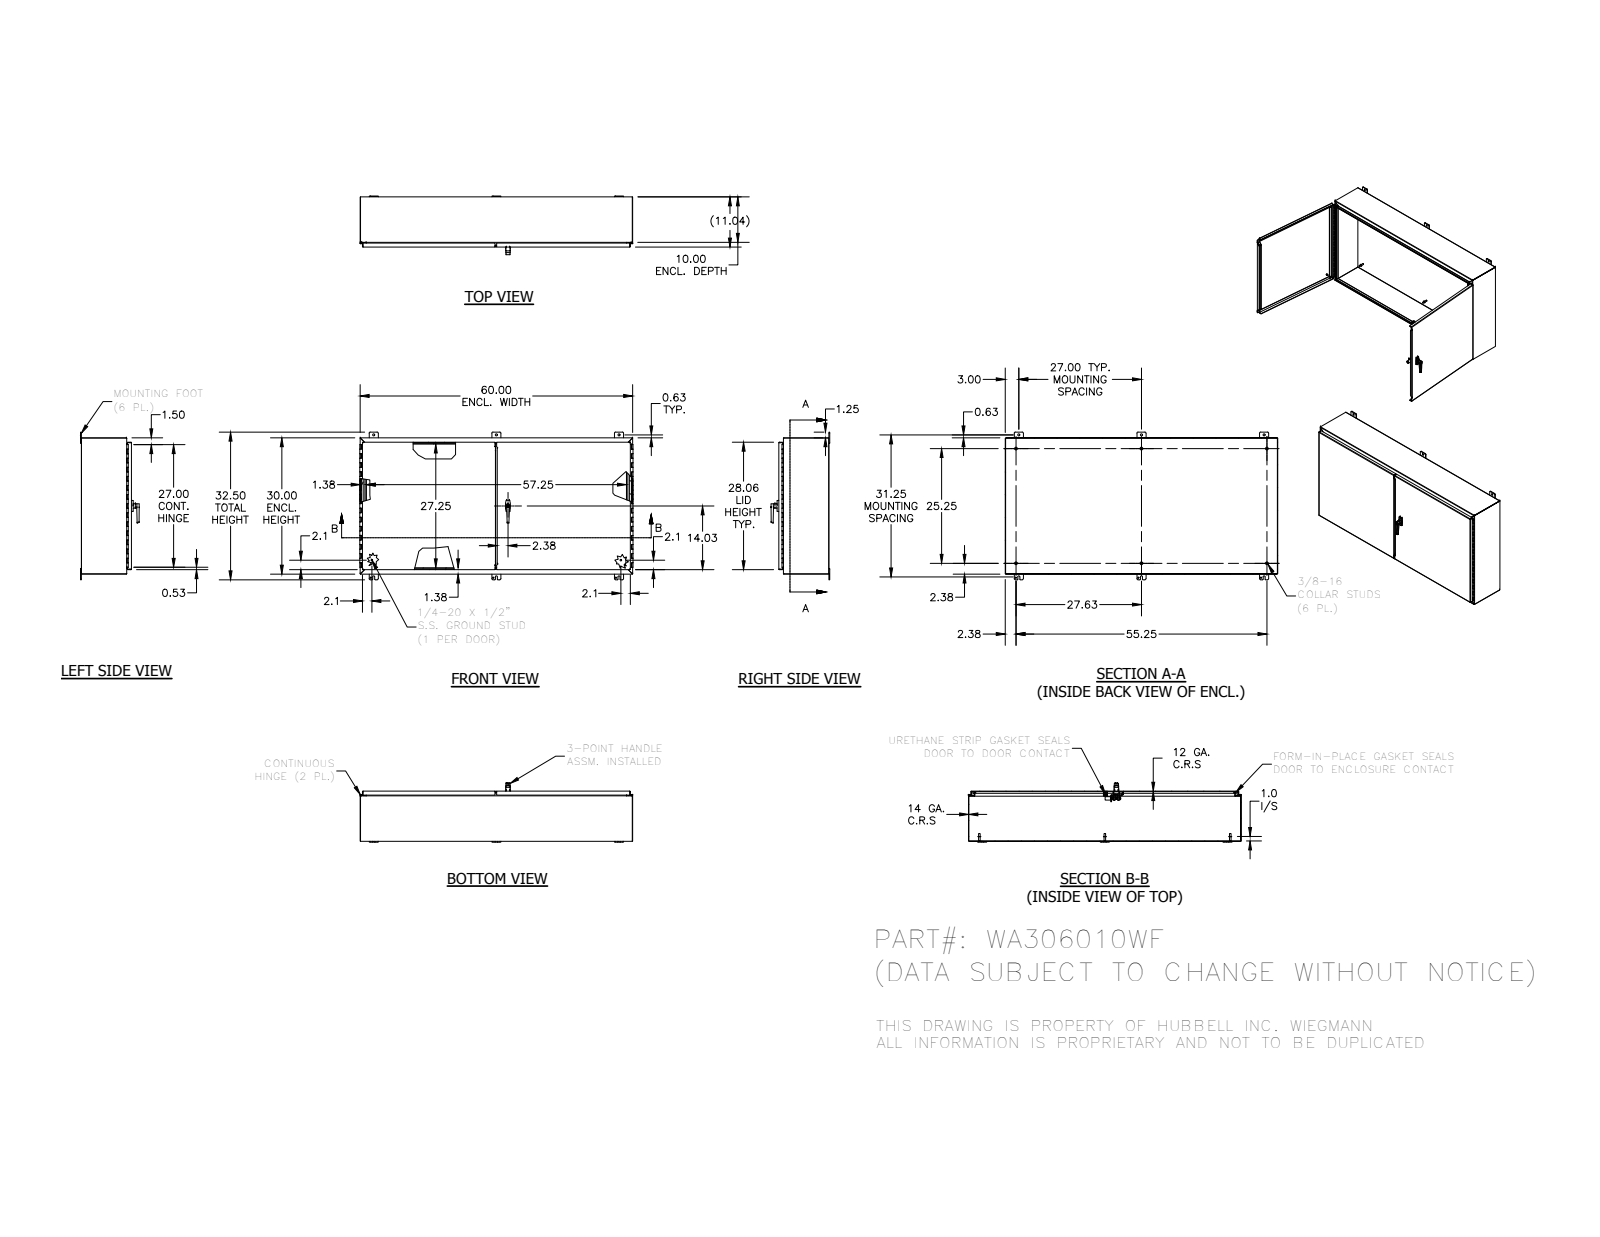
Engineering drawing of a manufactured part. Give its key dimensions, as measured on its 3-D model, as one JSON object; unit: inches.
{"part_name": "WA306010WF; WA306010WFLRS; 34840; WA306010WFBTB (+8 more)", "step_written_by": "Autodesk Inventor 2012 (AUTOMOTIVE_DESIGN)", "units": "inches", "bodies": {"solids": 60, "faces": 2548, "planar": 1400, "cylindrical": 658, "other": 490}, "overall_size": [60.148, 32.5, 12.919], "volume_in3": 540.1, "surface_area_in2": 12683, "round_holes": [[0.277, 8], [0.083, 6], [0.313, 6], [0.438, 6], [0.2, 4], [0.125, 2], [0.159, 2], [0.241, 2], [0.25, 2], [0.252, 2], [0.4, 2], [0.407, 2]], "round_bosses_or_shafts": [[0.157, 7], [0.625, 6], [0.33, 6], [0.25, 4], [0.115, 4], [1, 2], [0.563, 2], [0.527, 2]], "partial_cylinders_radius": [[0.031, 28], [0.25, 24], [0.008, 22], [0.016, 22], [0.105, 17], [0.01, 16], [0.05, 14], [0.125, 12]], "face_to_face_distances": [0.074, 0.094, 10.942, 10.868, 11.035, 10.961, 29.926, 59.926, 29.852, 30], "hole_center_spacings": [27, 40.361, 0.293, 1.593, 30, 0.201, 26.352, 27.724]}
